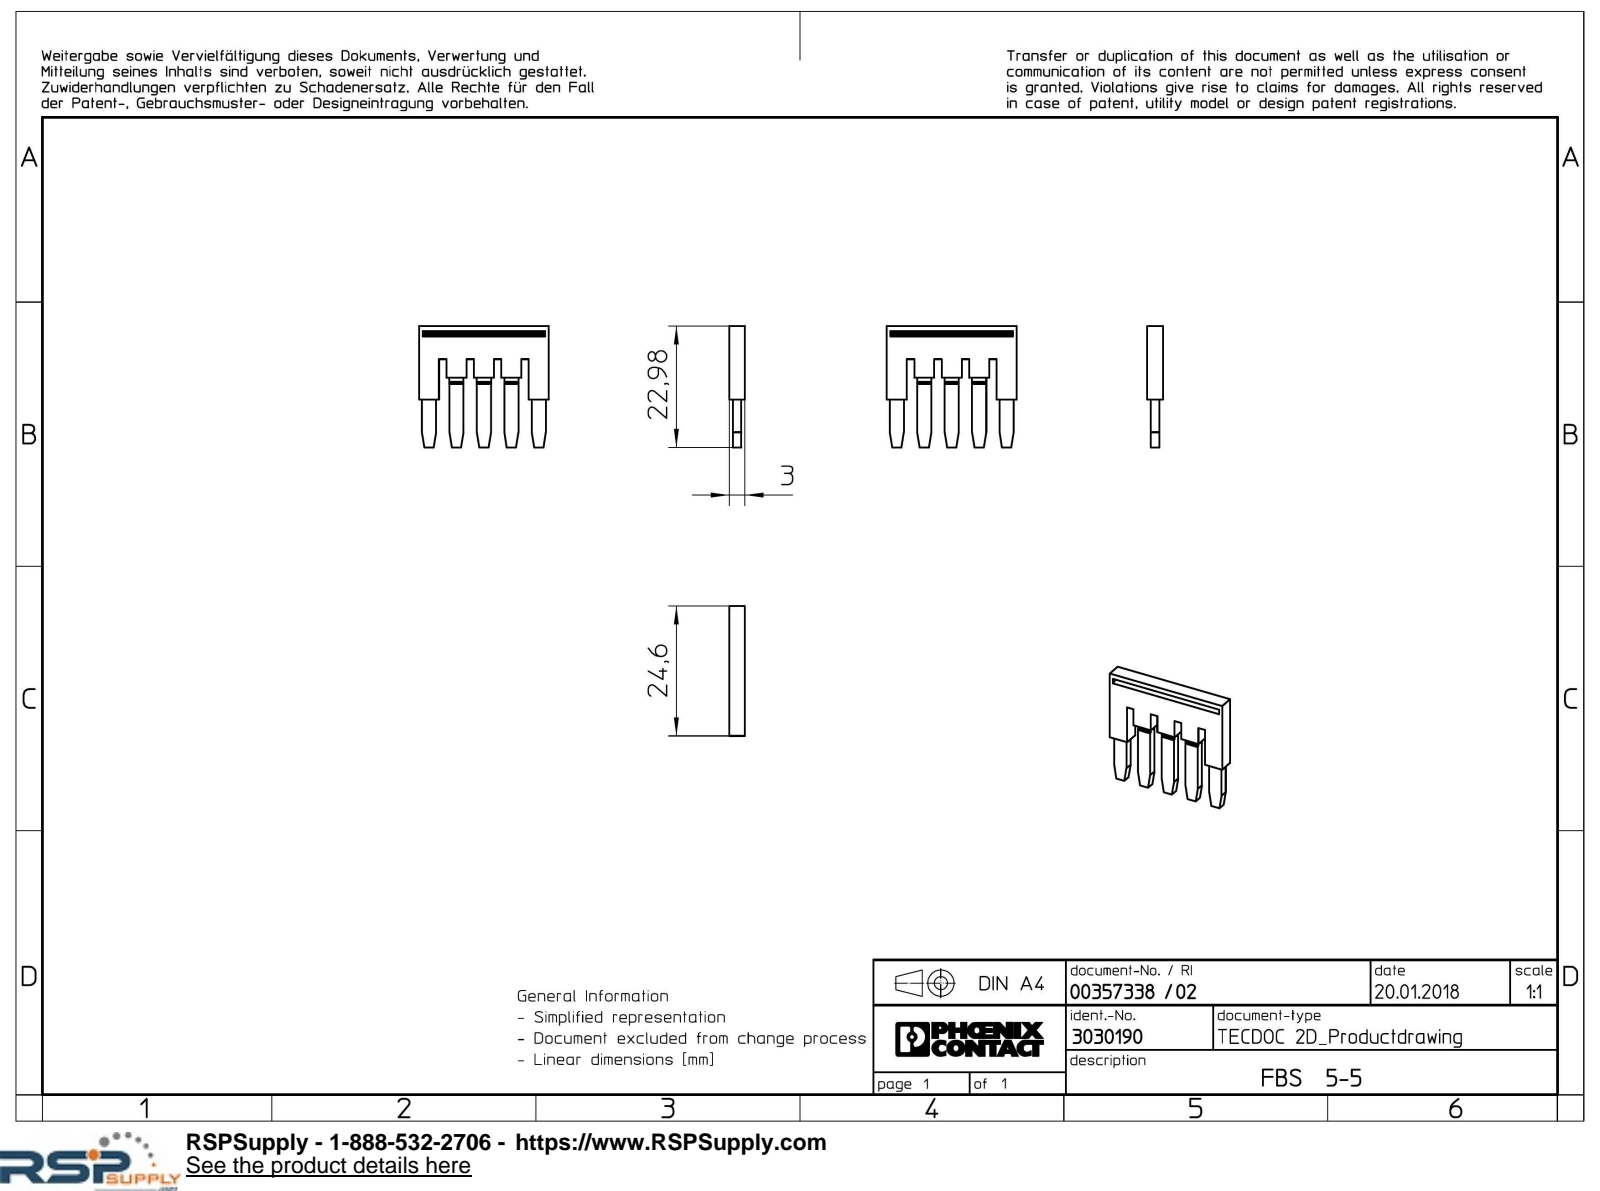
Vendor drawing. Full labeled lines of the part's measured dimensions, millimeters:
Part name (STEP PRODUCT): FBS_5_5-select
STEP written by: Creo Elements/Direct Modeling 20.1A 29-Sep-2018 (C) Parametric Technology GmbH (AUTOMOTIVE_DESIGN)
Units: millimetres
Bodies: 1 solid, 85 faces (85 planar, 0 cylindrical, 0 other)
Overall size (bounding box): 24.6 × 22.98 × 3
Volume: 962 mm³ · Surface area: 1 393 mm²
Main face-to-face distances: 0.7, 2.3, 3, 5.2, 1.6, 10.4, 0.56, 3.24, 8.44, 4.64
